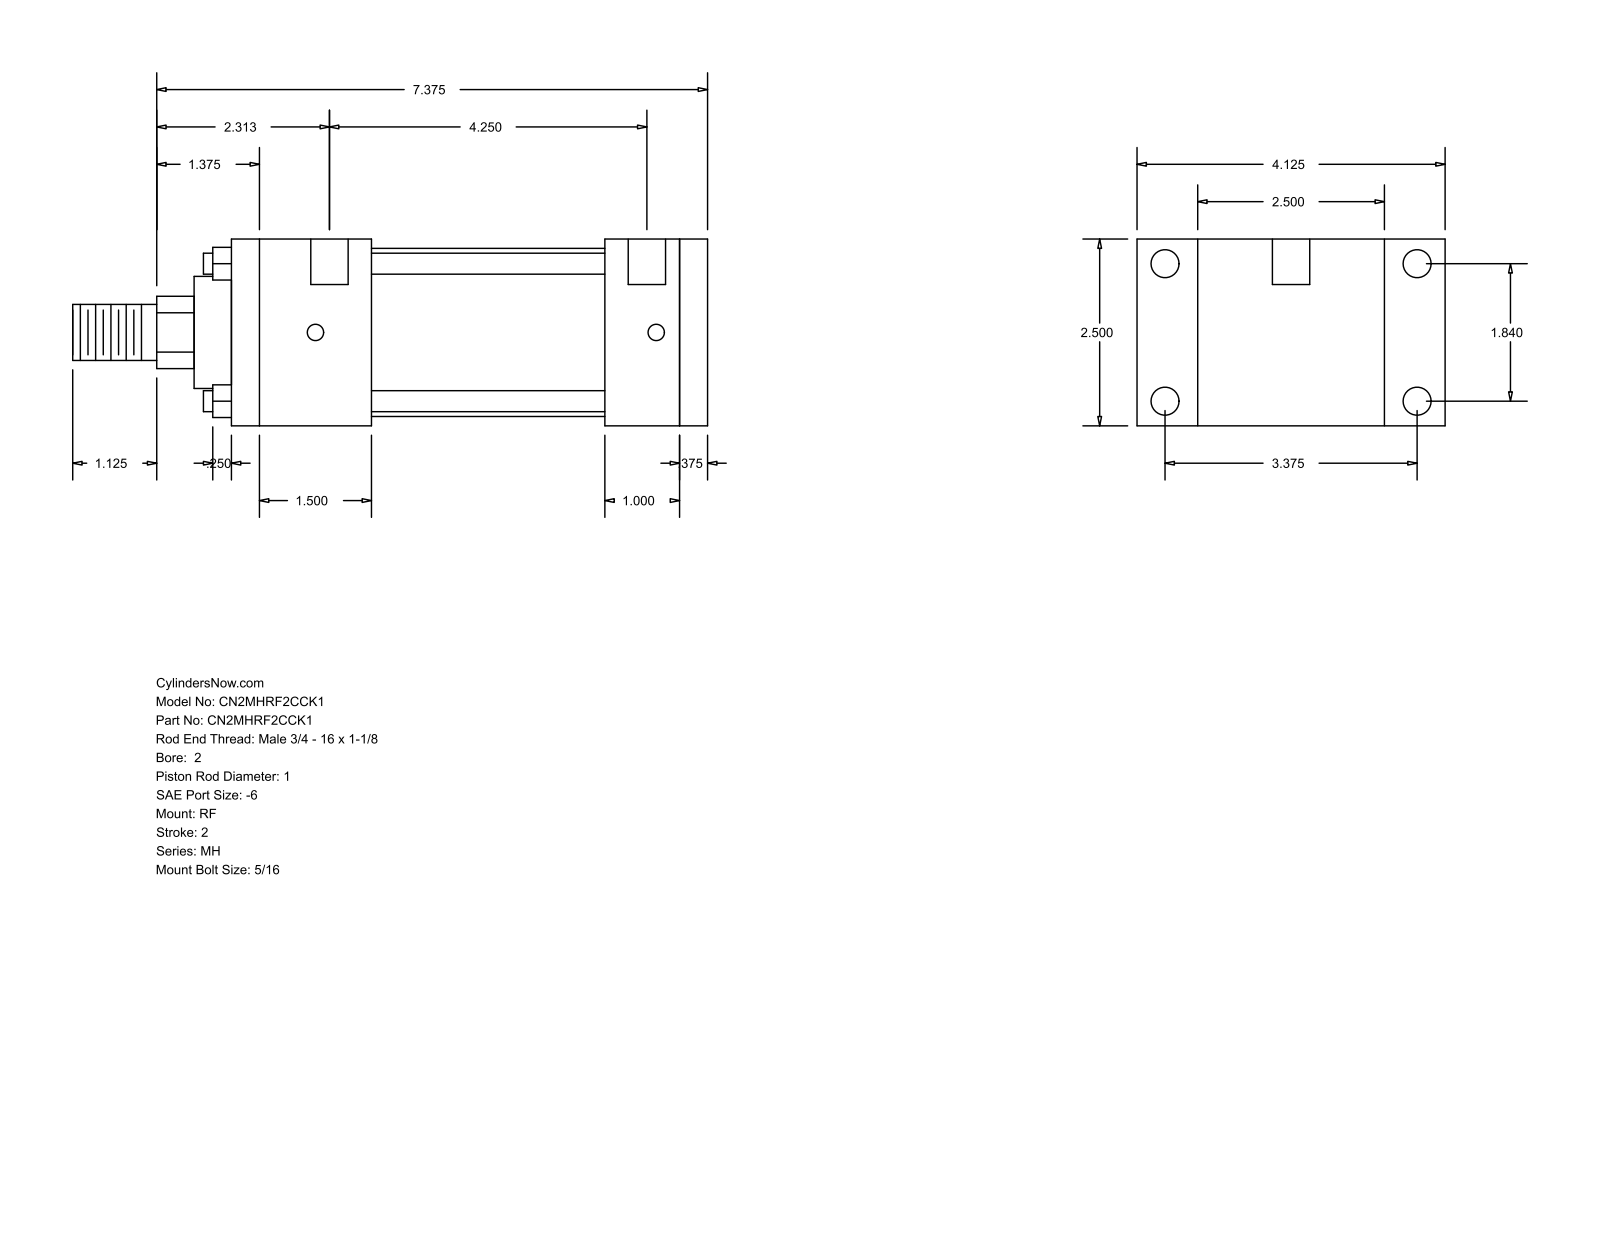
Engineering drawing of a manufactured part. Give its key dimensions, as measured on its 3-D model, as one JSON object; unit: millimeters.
{"part_name": "MH_RF__0200_1", "step_written_by": "GSSL Pune (CONFIG_CONTROL_DESIGN)", "units": "millimeters", "bodies": {"solids": 0, "faces": 92, "planar": 64, "cylindrical": 28, "other": 0}, "overall_size": [215.9, 104.78, 63.5], "round_holes": [[5.56, 4], [9.53, 4], [12.7, 2]], "round_bosses_or_shafts": [[7.14, 4], [57.15, 1], [38.1, 1], [25.4, 1], [19.05, 1]], "partial_cylinders_radius": [[12.29, 1]], "face_to_face_distances": [63.5, 161.92, 9.52, 152.4, 20.64, 25.4, 47.63, 127, 79.37, 104.77], "hole_center_spacings": [46.74, 85.72, 97.63, 115.88, 3.17, 4.76, 107.95, 111.12]}
